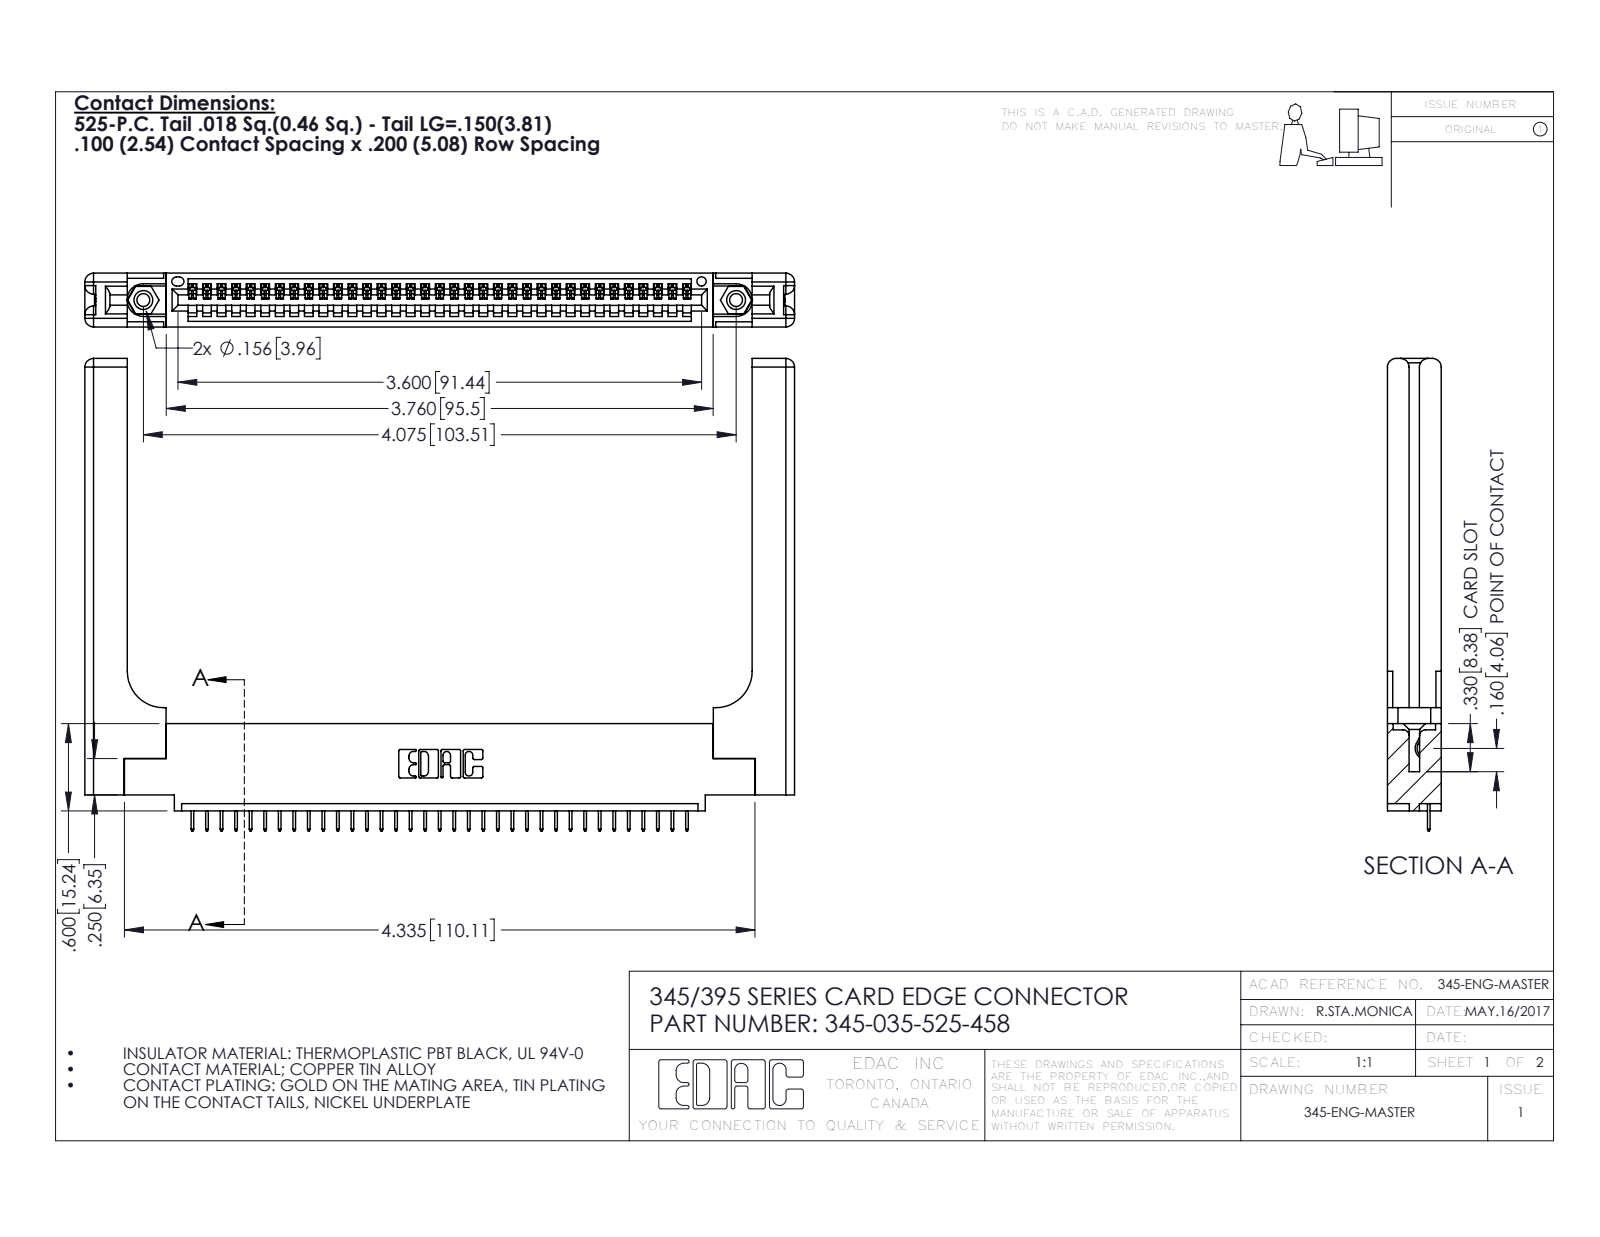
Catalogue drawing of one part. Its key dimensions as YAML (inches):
part_name: "345-035-525-458; 345-220-058_345-220-058; 345 Part_0.110 Offset - 0.156 Dia-TH; 345-292-001_345-293-125 (+1 more)"
step_written_by: "SolidWorks 2020 (CONFIG_CONTROL_DESIGN)"
units: inches
bodies: {solids: 40, faces: 2556, planar: 1842, cylindrical: 654, other: 60}
overall_size: [4.879, 3.247, 0.37]
volume: 1.221
surface_area: 31.15
round_holes:
  - {diameter: 0.089, count: 2}
  - {diameter: 0.125, count: 2}
  - {diameter: 0.156, count: 2}
  - {diameter: 0.064, count: 1}
round_bosses_or_shafts:
  - {diameter: 0.155, count: 2}
partial_cylinders:
  - {radius: 0.006, count: 70}
  - {radius: 0.01, count: 22}
  - {radius: 0.06, count: 16}
  - {radius: 0.007, count: 6}
  - {radius: 0.031, count: 6}
  - {radius: 0.026, count: 3}
  - {radius: 0.03, count: 2}
  - {radius: 0.031, count: 2}
face_to_face_distances: [0.37, 0.072, 0.298, 0.098, 0.272, 0.025, 0.2, 0.148, 0.15, 0.225]
hole_center_spacings: [0.27, 3.839, 4.075]
